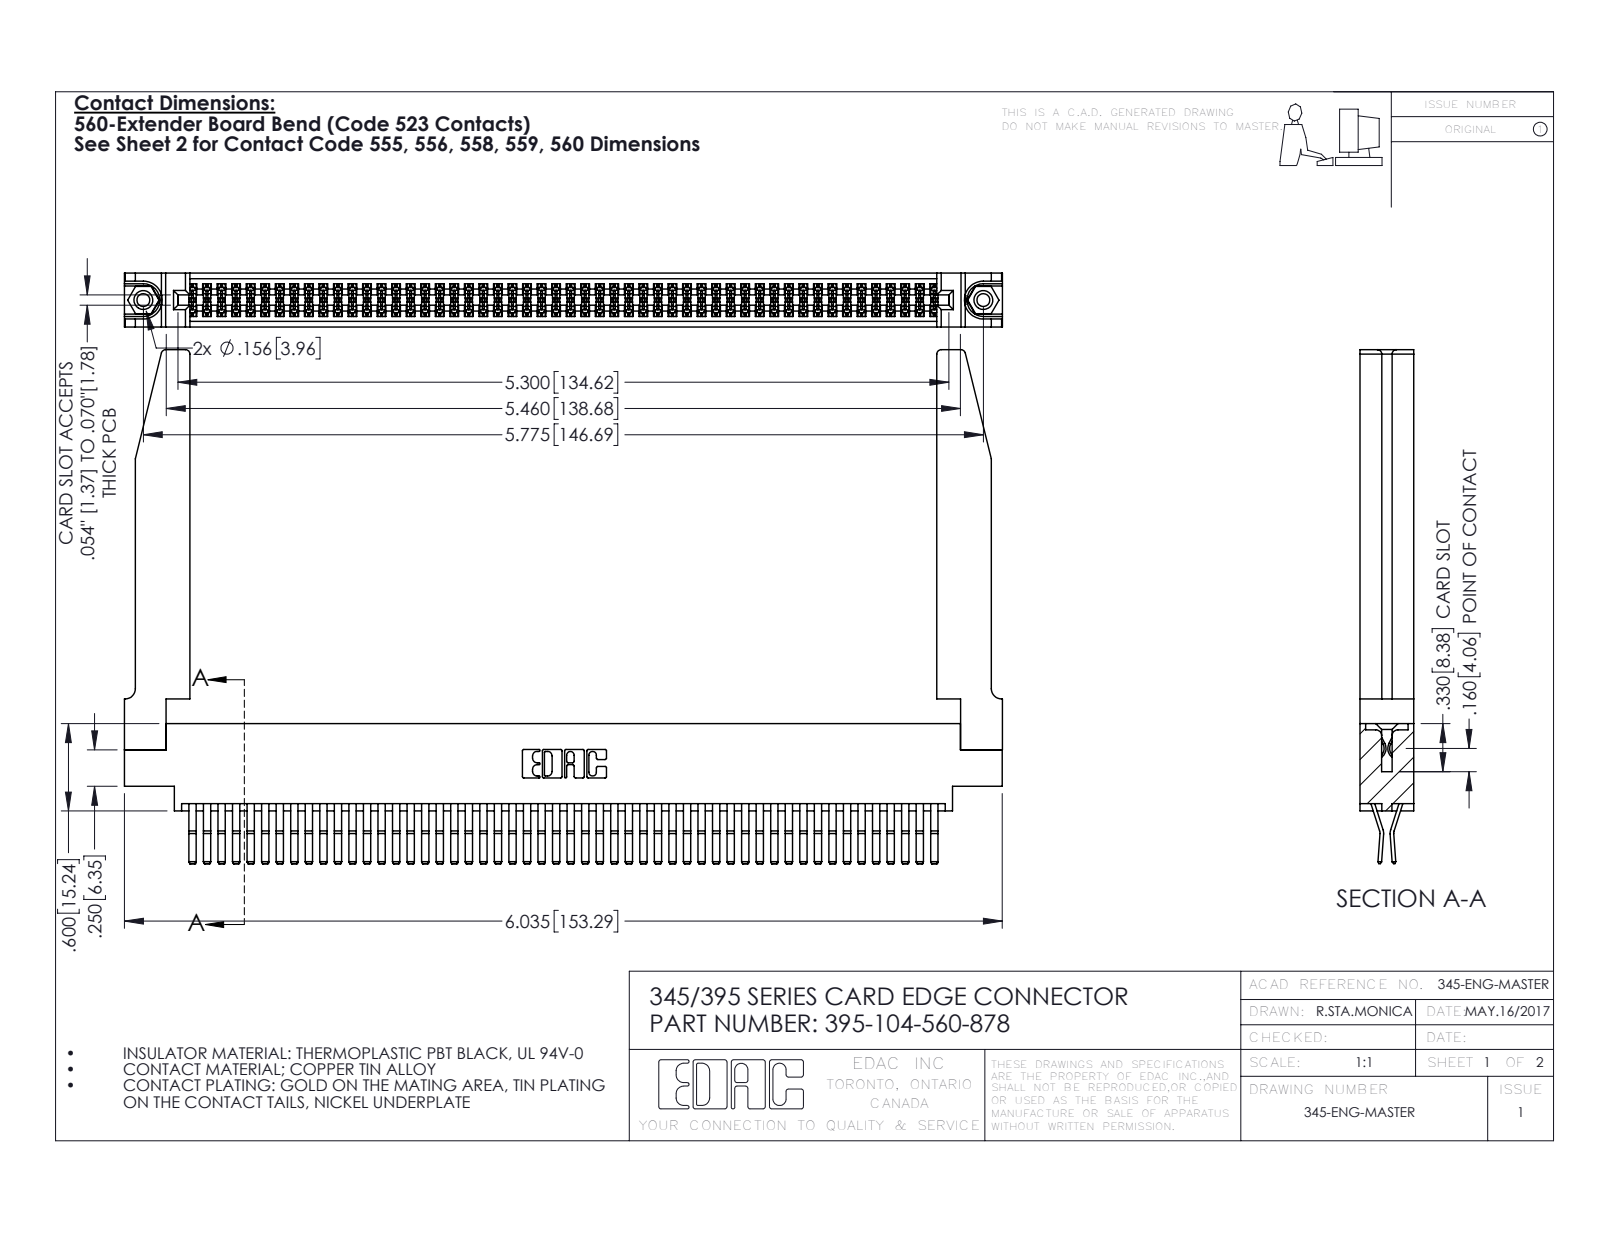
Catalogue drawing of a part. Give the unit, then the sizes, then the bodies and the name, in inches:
Units: inches
Overall size (bounding box): 6.036 × 3.532 × 0.37
Round holes (diameter × count): ⌀0.089 ×2, ⌀0.125 ×2, ⌀0.156 ×2, ⌀0.064 ×1
Round bosses / shafts (diameter × count): ⌀0.155 ×2
Partial cylindrical surfaces — rounded edges, fillets, slot ends (radius × count): R0.006 ×157, R0.01 ×22, R0.03 ×8, R0.007 ×6, R0.031 ×6, R0.026 ×3, R0.01 ×2, R0.014 ×2
Main face-to-face distances: 0.37, 0.072, 0.298, 0.025, 0.098, 0.272, 0.2, 0.225, 0.175, 0.15
Hole centre spacings: 0.27, 5.539, 5.775
Volume: 1.423 in³ · Surface area: 49.48 in²
Bodies: 109 solids, 5772 faces (3658 planar, 2062 cylindrical, 52 other)
Part name (STEP PRODUCT): 345 Part_0.170 Offset - 0.156 Dia-TH; 345-220-078_345-220-078; 345-250-001_345-250-001-102; 395-104-560-878 (+1 more)
STEP written by: SolidWorks 2016 (CONFIG_CONTROL_DESIGN)
